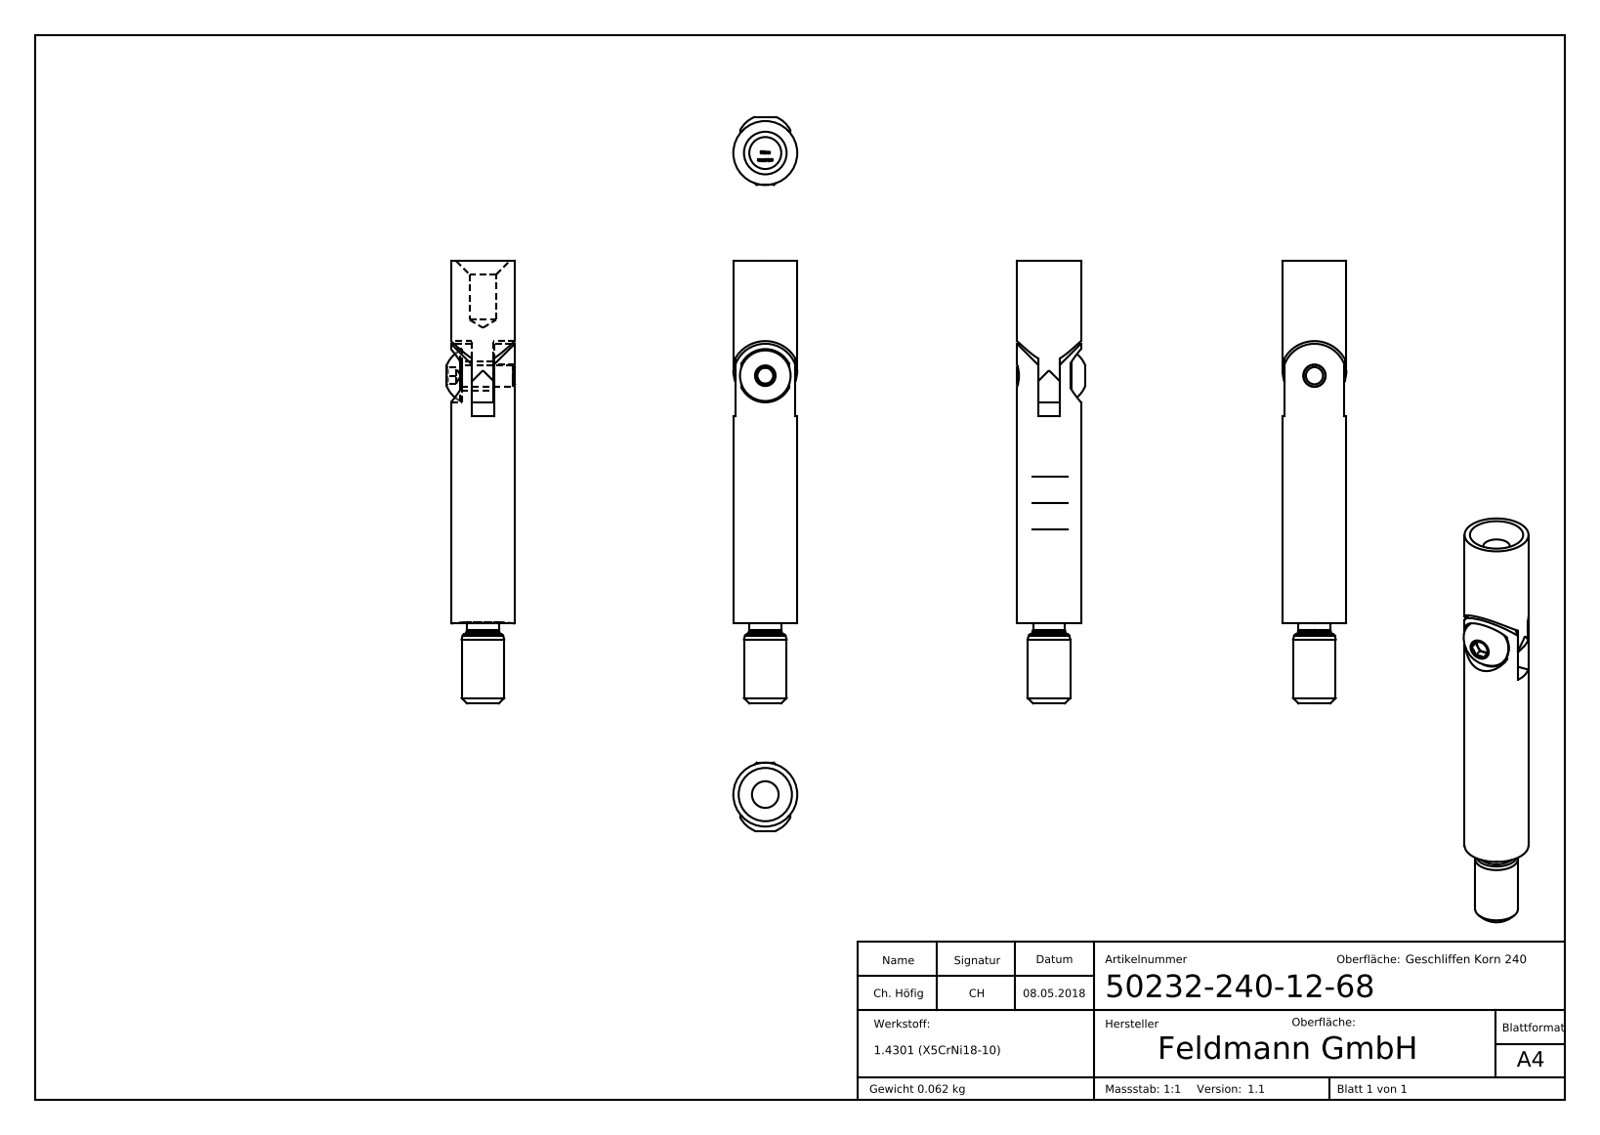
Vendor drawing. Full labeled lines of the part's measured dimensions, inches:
Part name (STEP PRODUCT): 50232-240-12-68 Teil2_50232-240-12-68 Teil2; 50232-240-12-68 Teil1_50232-240-12-68 Teil1; 50232-240-12-68; 50232-240-12-68 Teil1 (+3 more)
STEP written by: SolidWorks 2018 (CONFIG_CONTROL_DESIGN)
Units: inches
Bodies: 3 solids, 345 faces (171 planar, 17 cylindrical, 157 other)
Overall size (bounding box): 3.268 × 0.583 × 0.472
Volume: 0.476 in³ · Surface area: 6.784 in²
Round holes (diameter × count): ⌀0.165 ×1, ⌀0.197 ×1, ⌀0.217 ×1
Round bosses / shafts (diameter × count): ⌀0.472 ×1, ⌀0.374 ×1, ⌀0.315 ×1, ⌀0.236 ×1, ⌀0.158 ×1
Partial cylindrical surfaces — rounded edges, fillets, slot ends (radius × count): R0.236 ×2, R0.197 ×1, R0.256 ×1
Main face-to-face distances: 0.159, 0.161, 0.238, 0.077, 0.157, 0.236, 0.079, 1.142, 2.126, 3.268
